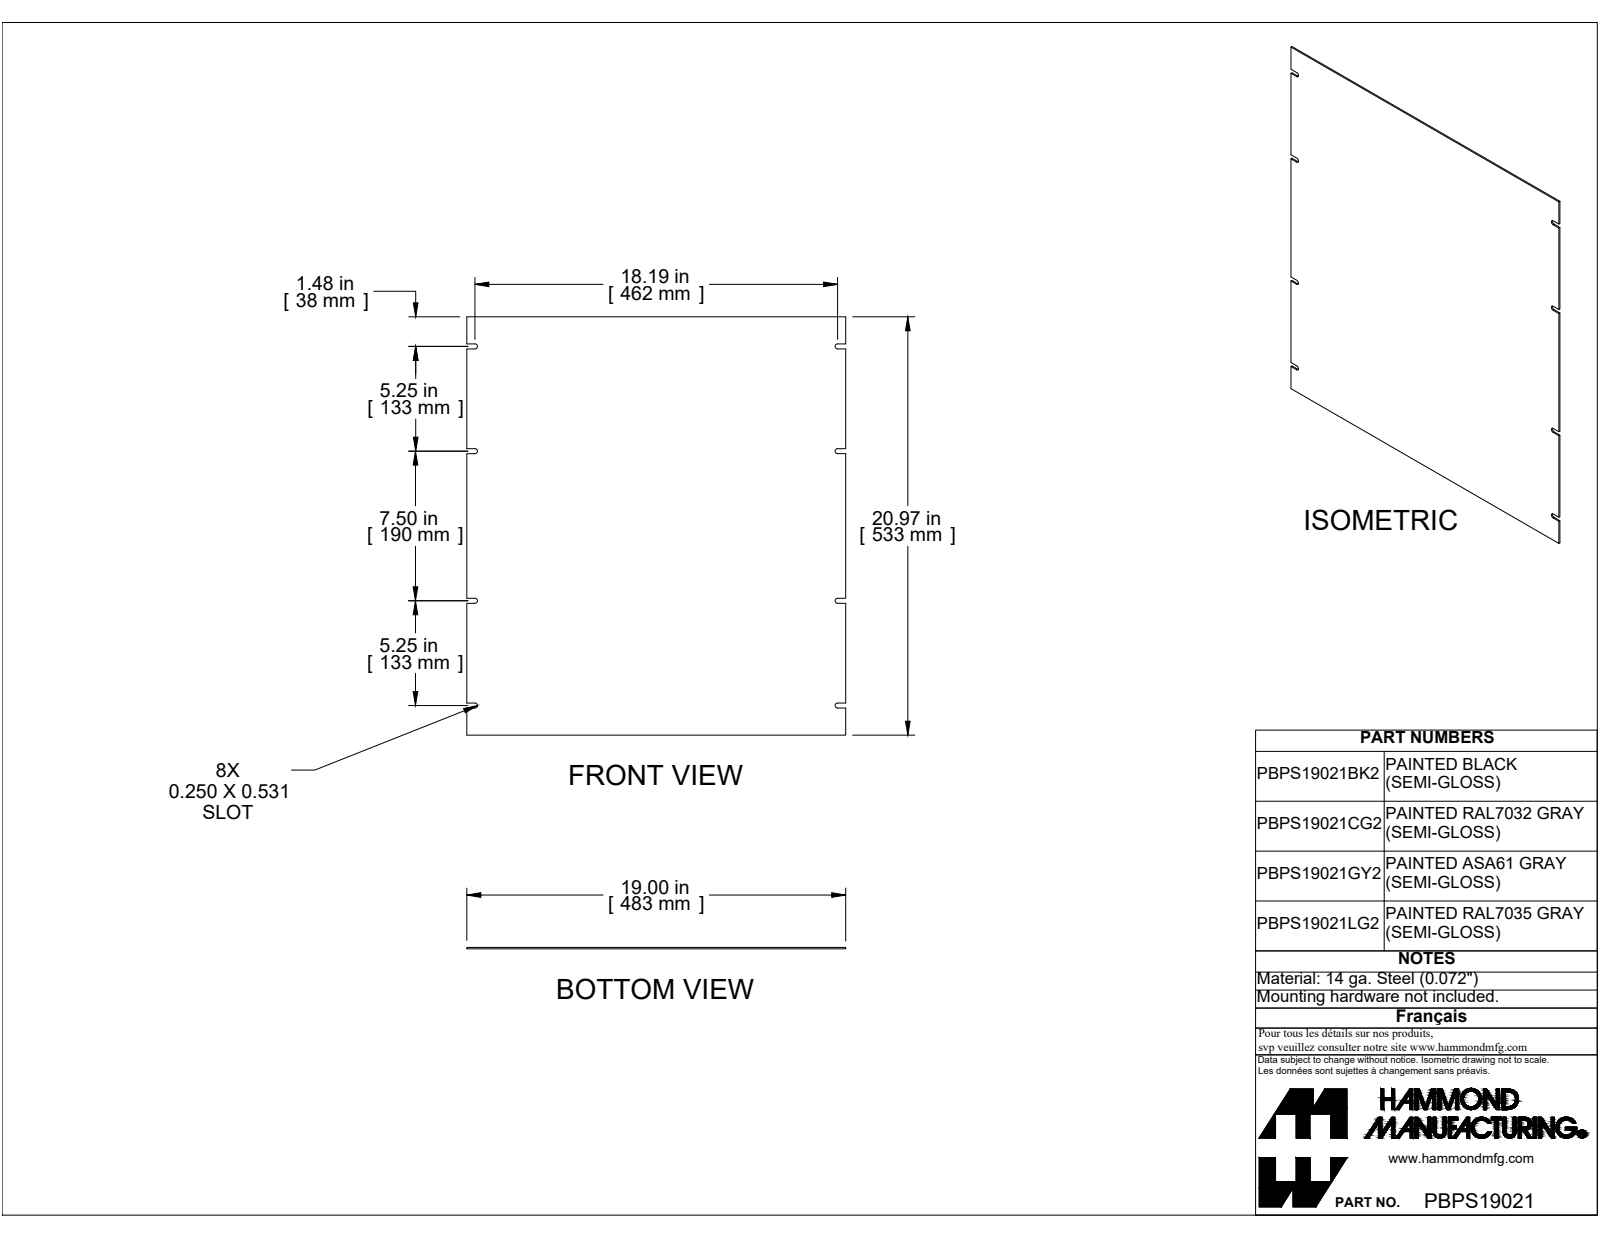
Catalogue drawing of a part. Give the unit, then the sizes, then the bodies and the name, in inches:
Units: inches
Overall size (bounding box): 20.968 × 19 × 0.072
Partial cylindrical surfaces — rounded edges, fillets, slot ends (radius × count): R0.125 ×8
Main face-to-face distances: 0.072, 19, 20.968, 0.25, 12.75, 5.25, 6.859, 14.109, 5.25, 5
Volume: 28.61 in³ · Surface area: 801.1 in²
Bodies: 1 solid, 38 faces (30 planar, 8 cylindrical, 0 other)
Part name (STEP PRODUCT): PBPS19021BK2
STEP written by: SolidWorks 2019 (CONFIG_CONTROL_DESIGN)
